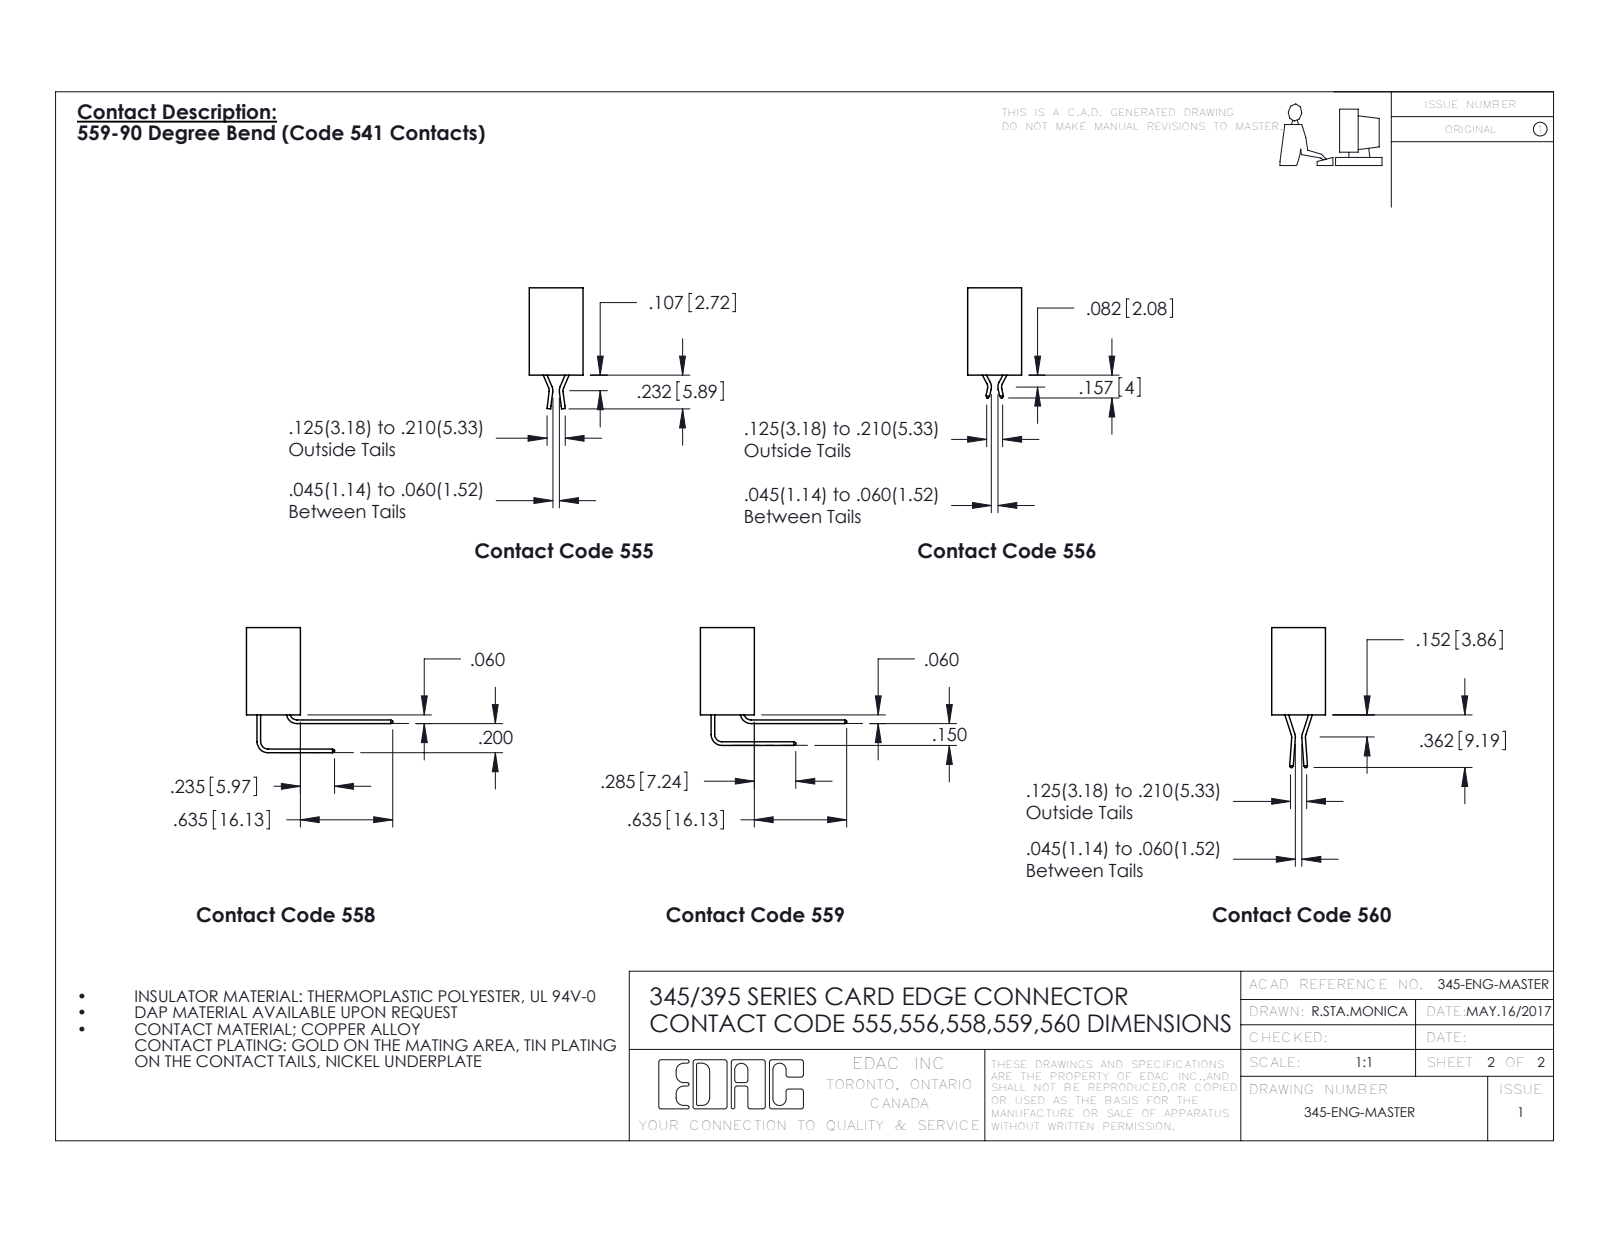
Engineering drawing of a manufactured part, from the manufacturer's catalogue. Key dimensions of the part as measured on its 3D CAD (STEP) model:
Part name (STEP PRODUCT): 395-066-558-412; 345-292-001_558 Tail - 2; 345 Part_0.110 Offset - Side Mount
STEP written by: SolidWorks 2016 (CONFIG_CONTROL_DESIGN)
Units: inches
Bodies: 67 solids, 4090 faces (2856 planar, 1234 cylindrical, 0 other)
Overall size (bounding box): 7.435 × 0.859 × 0.605
Volume: 1.11 in³ · Surface area: 39.89 in²
Round holes (diameter × count): ⌀0.128 ×2, ⌀0.064 ×1
Partial cylindrical surfaces — rounded edges, fillets, slot ends (radius × count): R0.006 ×132, R0.01 ×22, R0.007 ×6, R0.031 ×6, R0.026 ×3, R0.031 ×2, R0.04 ×2, R0.014 ×1
Main face-to-face distances: 0.072, 0.298, 0.37, 0.2, 0.098, 0.272, 0.025, 0.225, 0.149, 0.072
Hole centre spacings: 7.175
